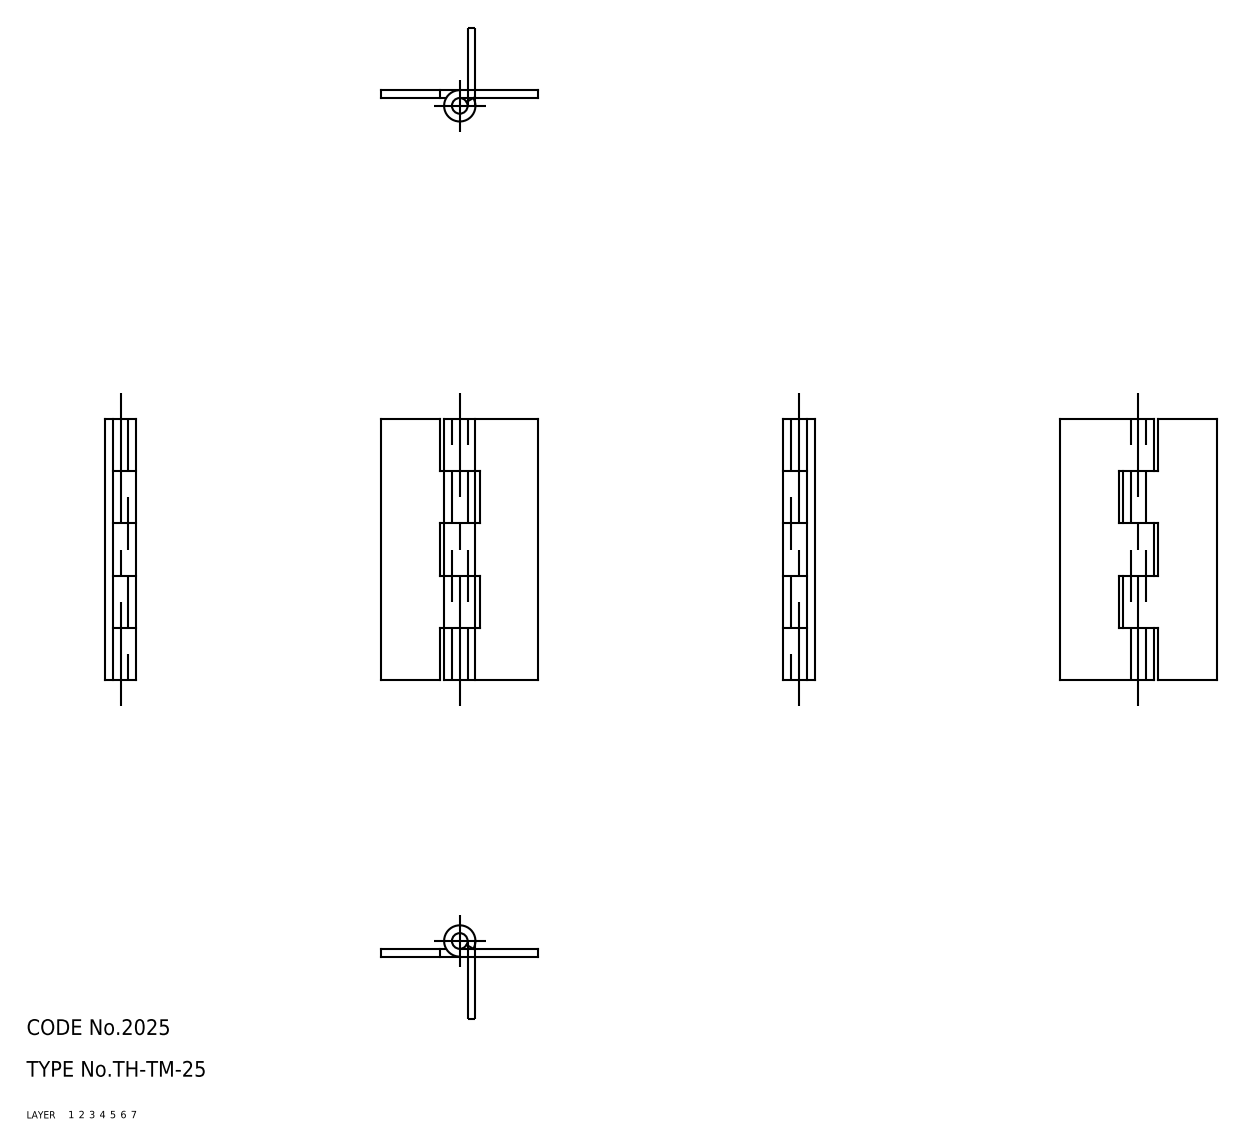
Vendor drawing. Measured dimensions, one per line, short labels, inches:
name: hinge piece_B; hinge piece_A; shaft; TH_TM_25_22209_36
written by: CADfix (AUTOMOTIVE_DESIGN)
unit: in
bodies: 3 solids, 42 faces (0 planar, 0 cylindrical, 42 other)
size: 1.969 × 1.181 × 0.236
volume: 0.195 in³; area: 7.564 in²
